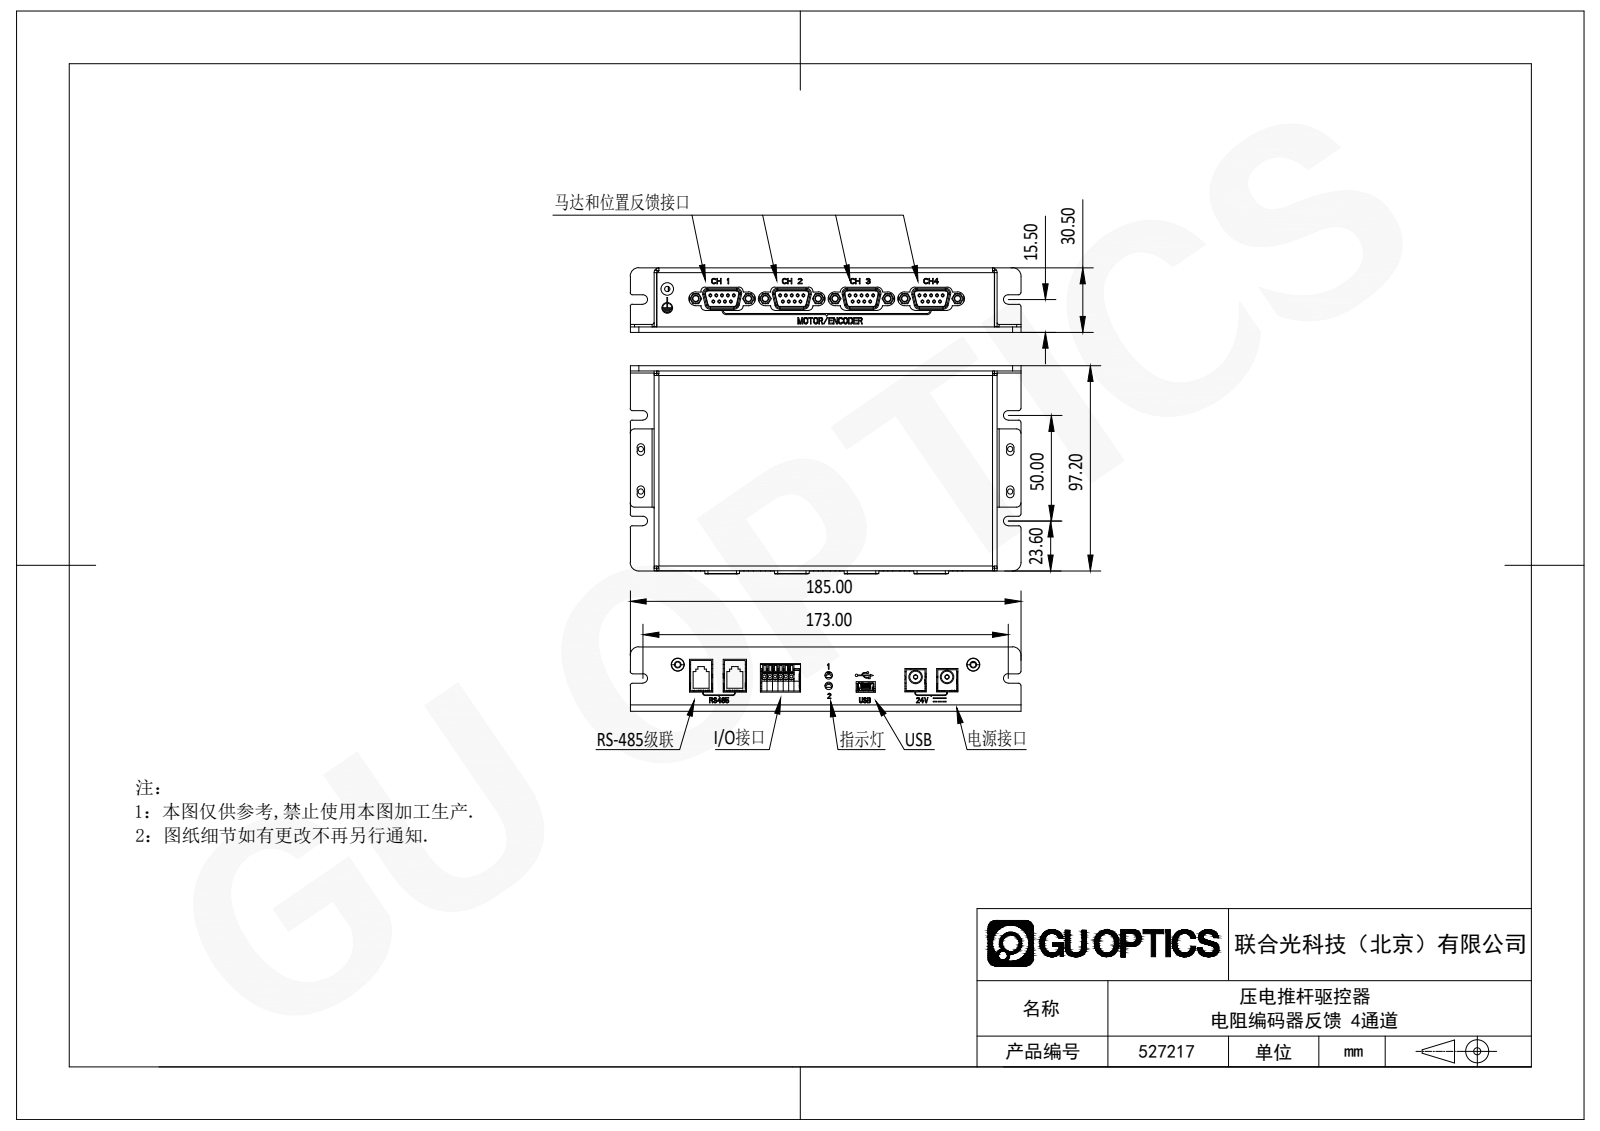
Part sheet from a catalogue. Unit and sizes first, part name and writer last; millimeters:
Units: millimetres
Overall size (bounding box): 185 × 98.61 × 30.5
Round holes (diameter × count): ⌀0.3 ×254, ⌀1 ×80, ⌀1.2 ×15, ⌀2.5 ×13, ⌀0.9 ×10, ⌀2.6 ×8, ⌀3.25 ×8, ⌀4.1 ×8, ⌀1.1 ×6, ⌀1.5 ×6, ⌀3 ×5, ⌀0.45 ×4
Round bosses / shafts (diameter × count): ⌀0.65 ×36, ⌀4 ×8, ⌀0.9 ×8, ⌀5.38 ×6, ⌀1.29 ×6, ⌀2.29 ×4, ⌀0.8 ×4, ⌀0.6 ×4
Partial cylindrical surfaces — rounded edges, fillets, slot ends (radius × count): R0.2 ×58, R0.1 ×44, R0.5 ×38, R1.89 ×32, R1 ×30, R1.5 ×24, R0.25 ×16, R1.8 ×16
Main face-to-face distances: 1.2, 2.5, 26.8, 28, 30.5, 29.3, 20.91, 9.59, 7.09, 19.71
Hole centre spacings: 2.77, 3.16, 33, 5.54, 31.75, 34.51, 30.23, 1
Volume: 128 200 mm³ · Surface area: 151 908 mm²
Bodies: 49 solids, 7548 faces (4600 planar, 1756 cylindrical, 1192 other)
Part name (STEP PRODUCT): 527217
STEP written by: SolidWorks 2020 (CONFIG_CONTROL_DESIGN)
